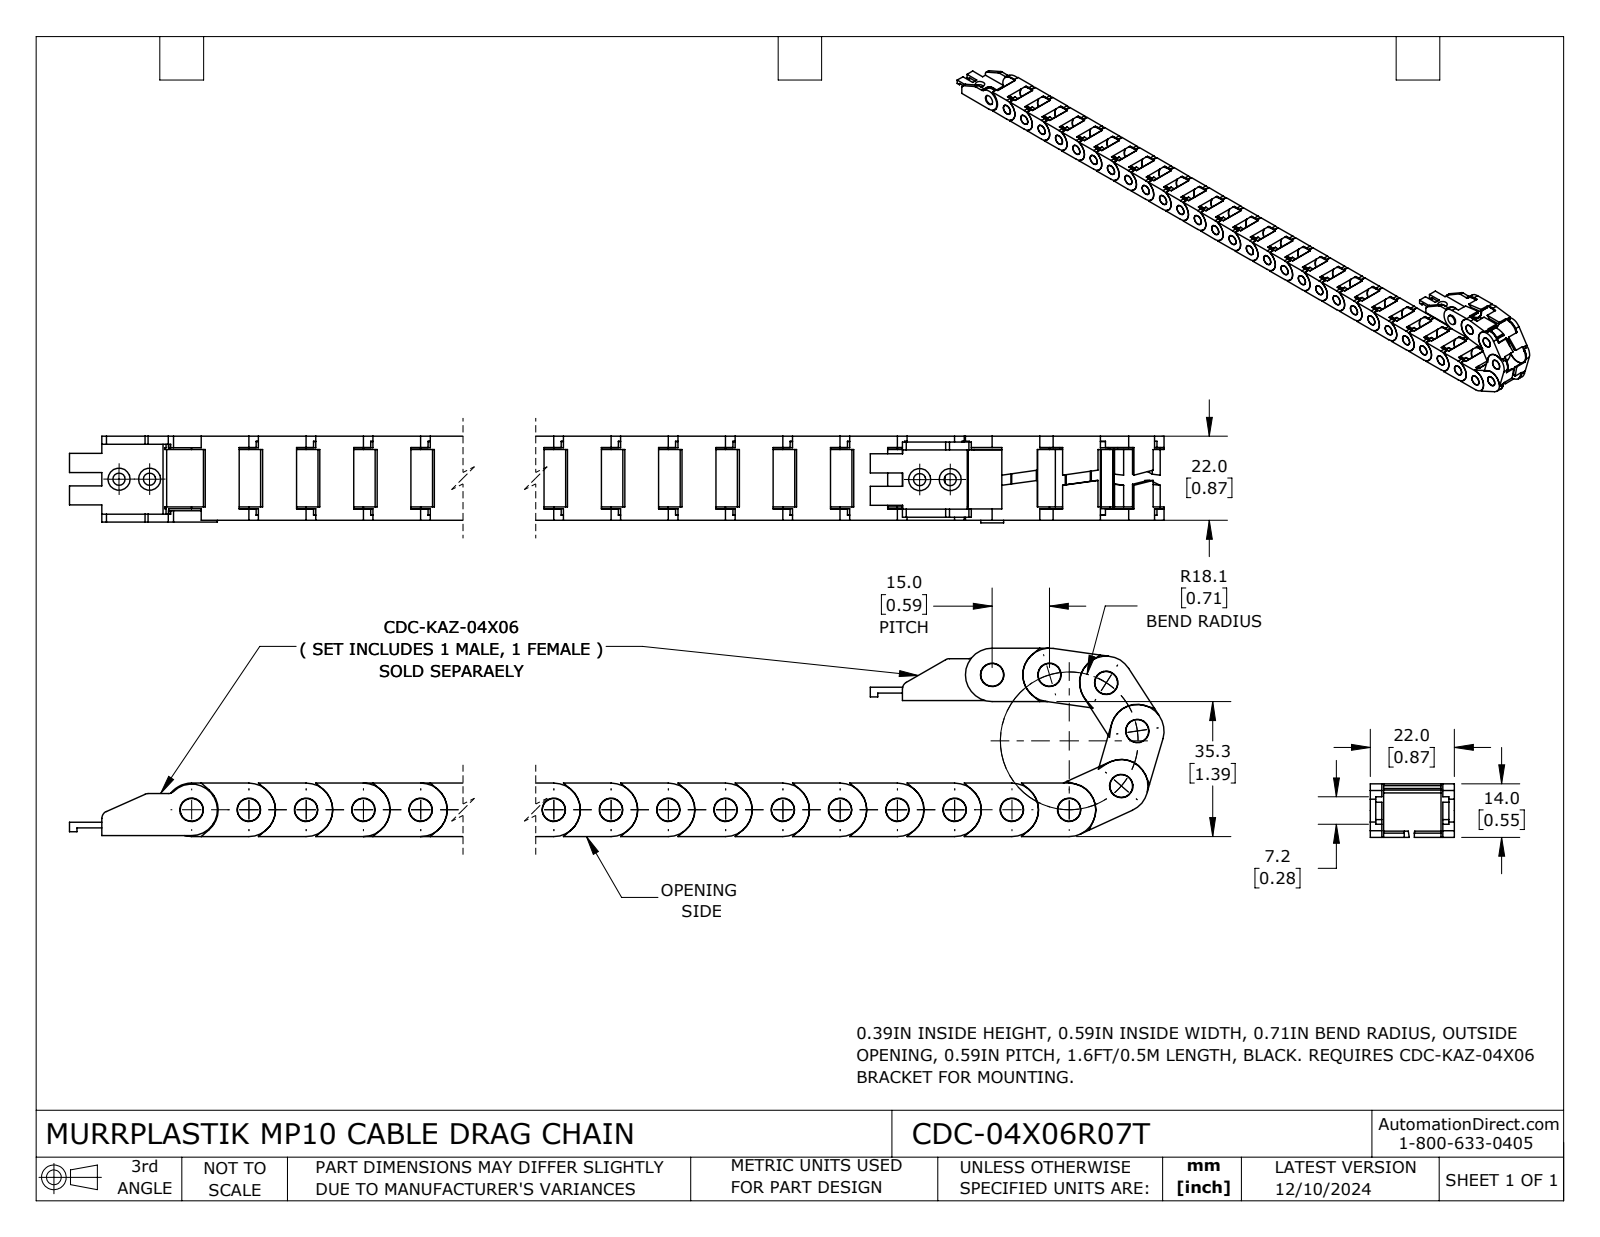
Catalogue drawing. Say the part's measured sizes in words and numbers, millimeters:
The part is named "CDC-04X06R07T". Its 3-D file was written by "SolidWorks 2024 (AUTOMOTIVE_DESIGN)". It is 34 solids with 2317 faces: 1572 planar, 741 cylindrical and 4 other. Overall it measures 476.9 by 49.3 by 22.7 millimeters. Its volume is 61 470 cubic millimeters and its surface area 86 190 square millimeters. Round holes: 32 of diameter 6.1, 4 of diameter 3.2, 1 of diameter 6.2. Round bosses or shafts: 33 of diameter 6, 28 of diameter 14. Partial cylindrical surfaces (rounded edges, fillets, slot ends): 160 of radius 0.5, 36 of radius 7, 32 of radius 3.6, 32 of radius 11.6, 8 of radius 7, 6 of radius 2, 2 of radius 1, 2 of radius 6.8. The main face-to-face distances are 3.5, 18.5, 22, 1.6, 15, 14, 2.2, 0.5, 1.3, 17.7. The hole center spacings are 15, 30, 45, 60, 75, 90, 105, 120.
